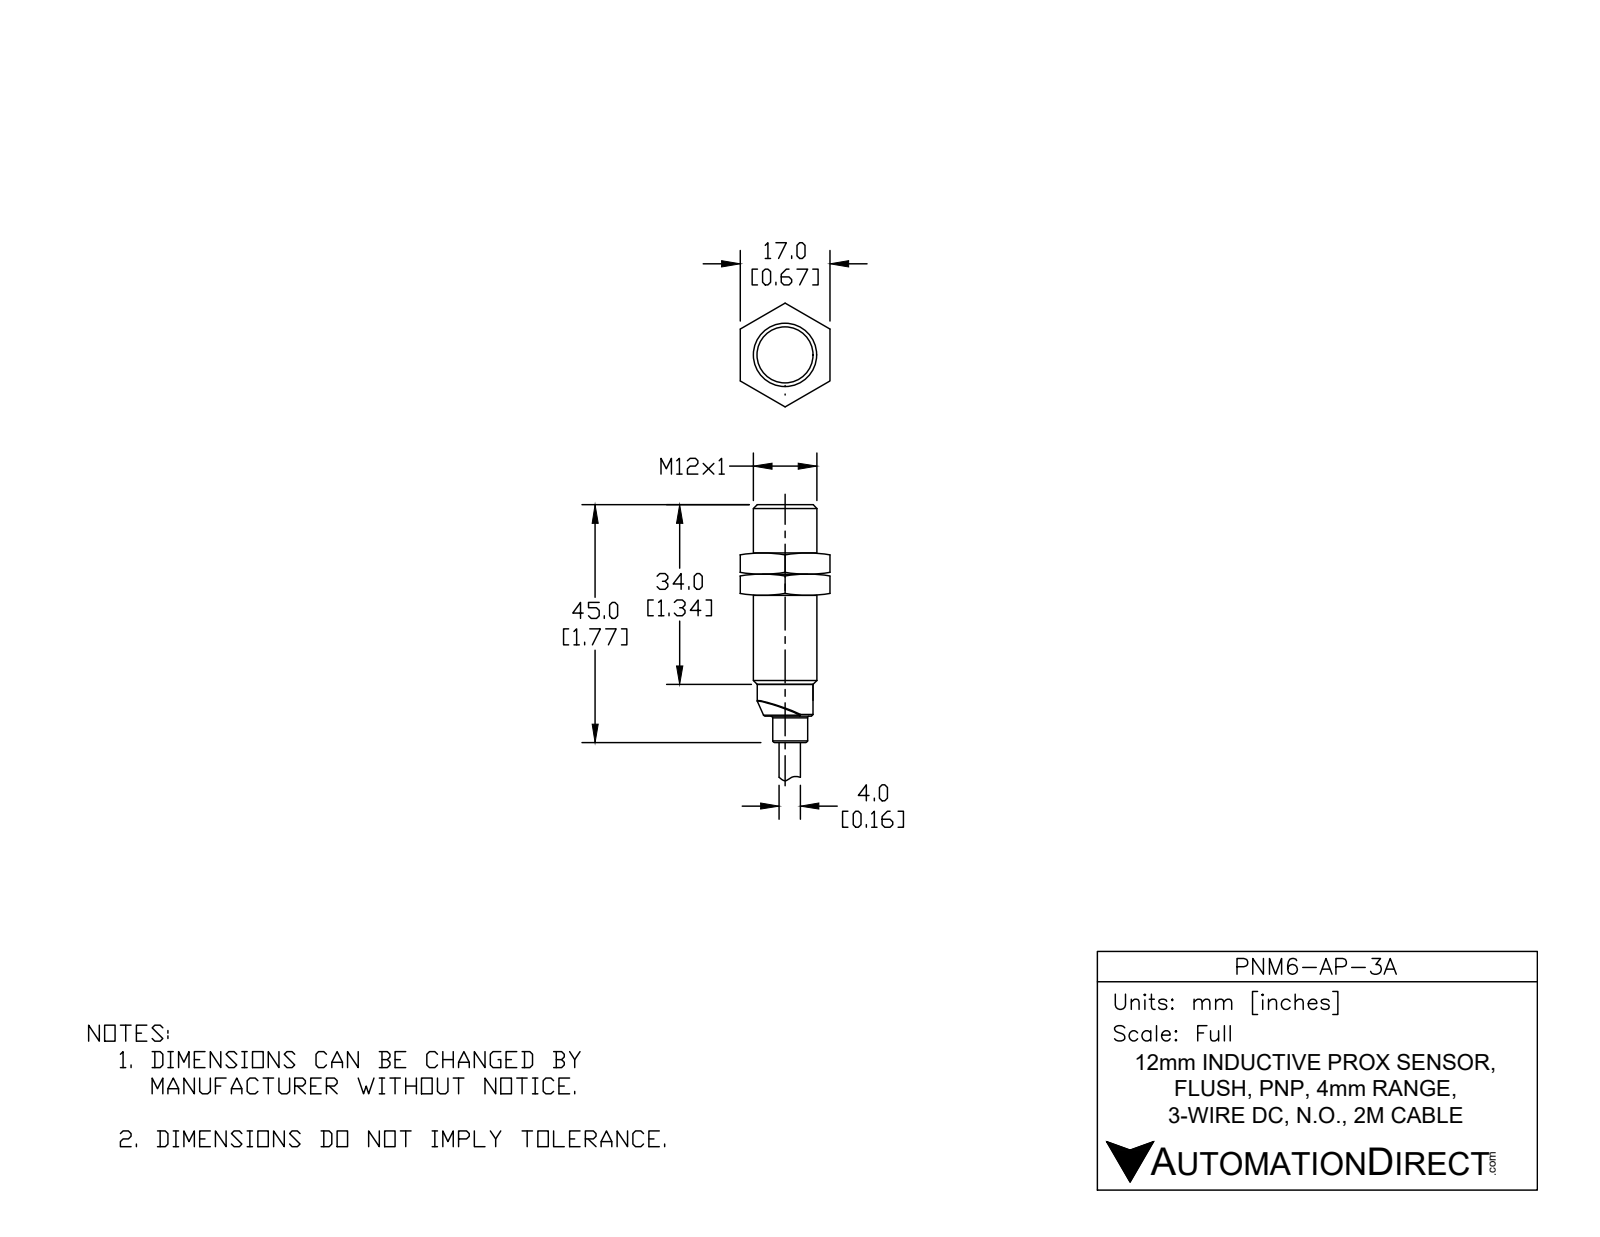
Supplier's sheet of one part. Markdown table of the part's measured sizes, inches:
| quantity | value |
| --- | --- |
| part name | PNM6-AP-3A |
| STEP written by | SolidWorks 2017 (AUTOMOTIVE_DESIGN) |
| units | inches |
| bodies | 1 solid, 59 faces (13 planar, 23 cylindrical, 23 other) |
| overall size | 3.772 × 0.472 × 0.472 |
| volume | 0.313 in³ |
| surface area | 4.04 in² |
| round holes (diameter × count) | 0.161 × 1 |
| round bosses / shafts (diameter × count) | 0.049 × 3, 0.472 × 1, 0.417 × 1, 0.415 × 1, 0.26 × 1, 0.157 × 1 |
| partial cylindrical surfaces (radius × count) | 0.025 × 1, 0.077 × 1 |
| main face-to-face distances | 1.575, 1.772, 0.197, 3.772, 2.197, 2, 1.457, 0.118, 0.315, 2.315 |
